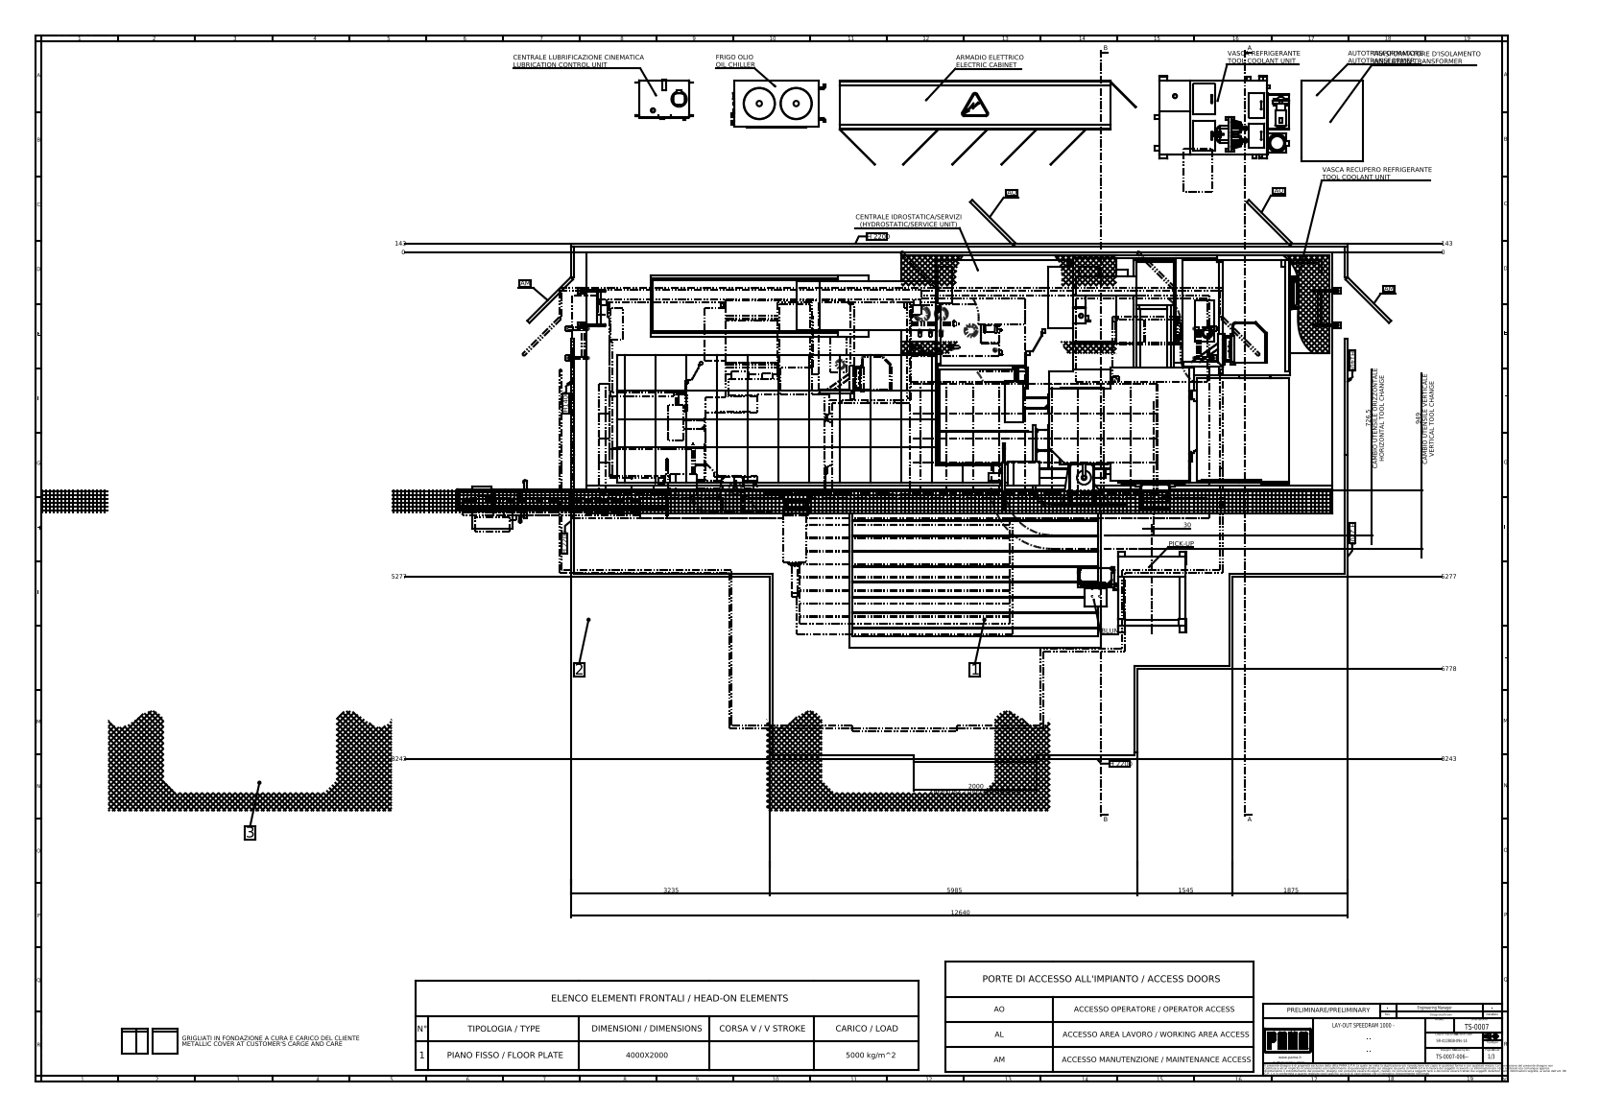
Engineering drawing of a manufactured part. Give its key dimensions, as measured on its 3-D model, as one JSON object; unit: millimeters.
{"part_name": "S003251_ISO 50 - RIPOSO; S003244_SRAM 4-412; S003207_X=5000; LAYOUT SPEEDRAM PMS V2.0 (+8 more)", "step_written_by": "SolidWorks 2023 (AUTOMOTIVE_DESIGN)", "units": "millimeters", "bodies": {"solids": 397, "faces": 6335, "planar": 4445, "cylindrical": 1427, "other": 463}, "overall_size": [16140, 14057.4, 7912.5], "volume_mm3": 412000000000, "surface_area_mm2": 1597000000, "round_holes": [[35, 64], [69.6, 63], [37.2, 18], [30, 9], [13, 8], [14, 8], [8, 6], [12.5, 4], [56.66, 4], [60, 4], [25.6, 3], [50, 3]], "round_bosses_or_shafts": [[42.4, 18], [20, 14], [40, 11], [9, 10], [55, 8], [66.3, 7], [60, 6], [35, 6]], "partial_cylinders_radius": [[5, 128], [15, 53], [8, 52], [35, 26], [6, 25], [3, 21], [4, 21], [10, 20]], "face_to_face_distances": [2000, 50, 1247, 753, 5, 10, 13986, 16140, 2650, 2700], "hole_center_spacings": [273.13, 500, 1235.56, 758.02, 1423.59, 1000, 130, 260]}
